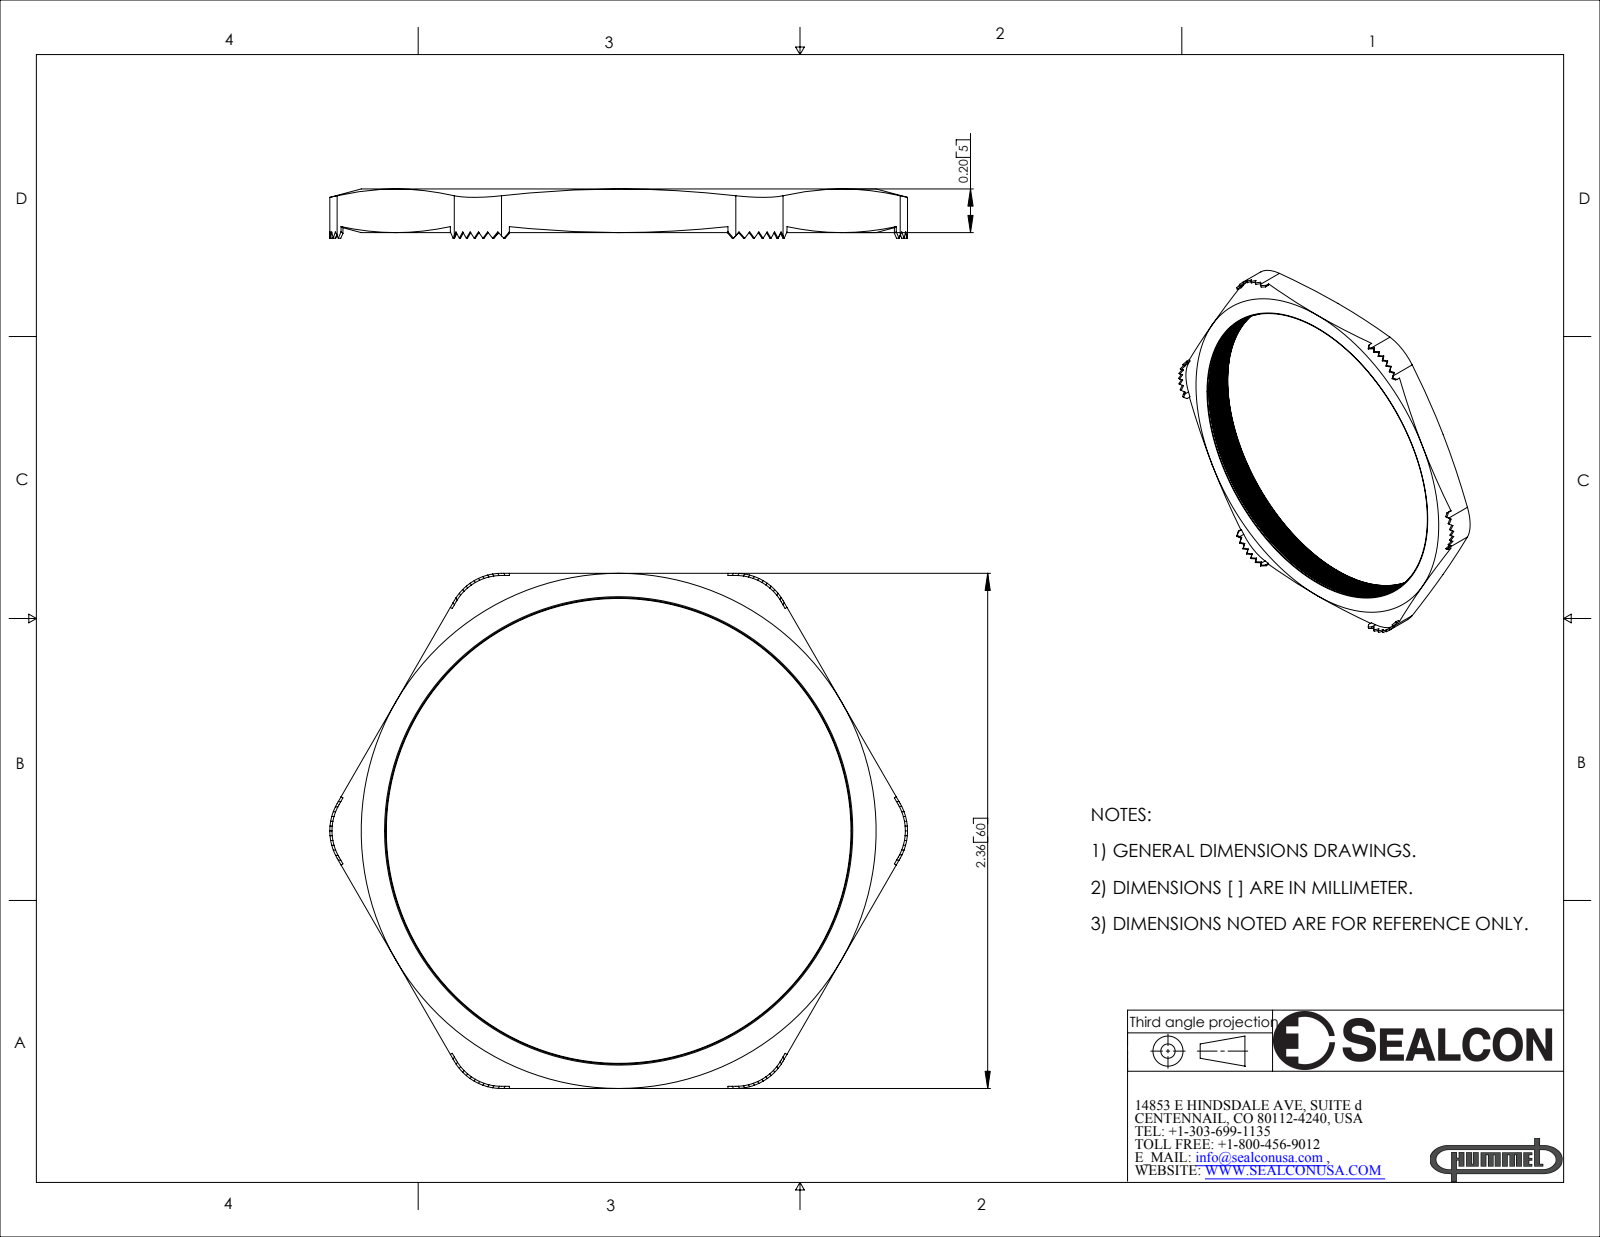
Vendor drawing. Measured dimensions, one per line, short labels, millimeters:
name: NP-42-BE
written by: SolidWorks 2007 (CONFIG_CONTROL_DESIGN)
unit: mm
bodies: 1 solid, 248 faces (116 planar, 46 cylindrical, 86 other)
size: 67.3 × 59.9 × 5.7
volume: 3 790 mm³; area: 4 264 mm²
holes: 1× ⌀54.1
rounds: 6× R6.1, 6× R6.4
face distances: 5.1, 59.9, 59.7, 0.9, 1.8, 0.9, 59.4, 2.7, 4.5, 3.6
